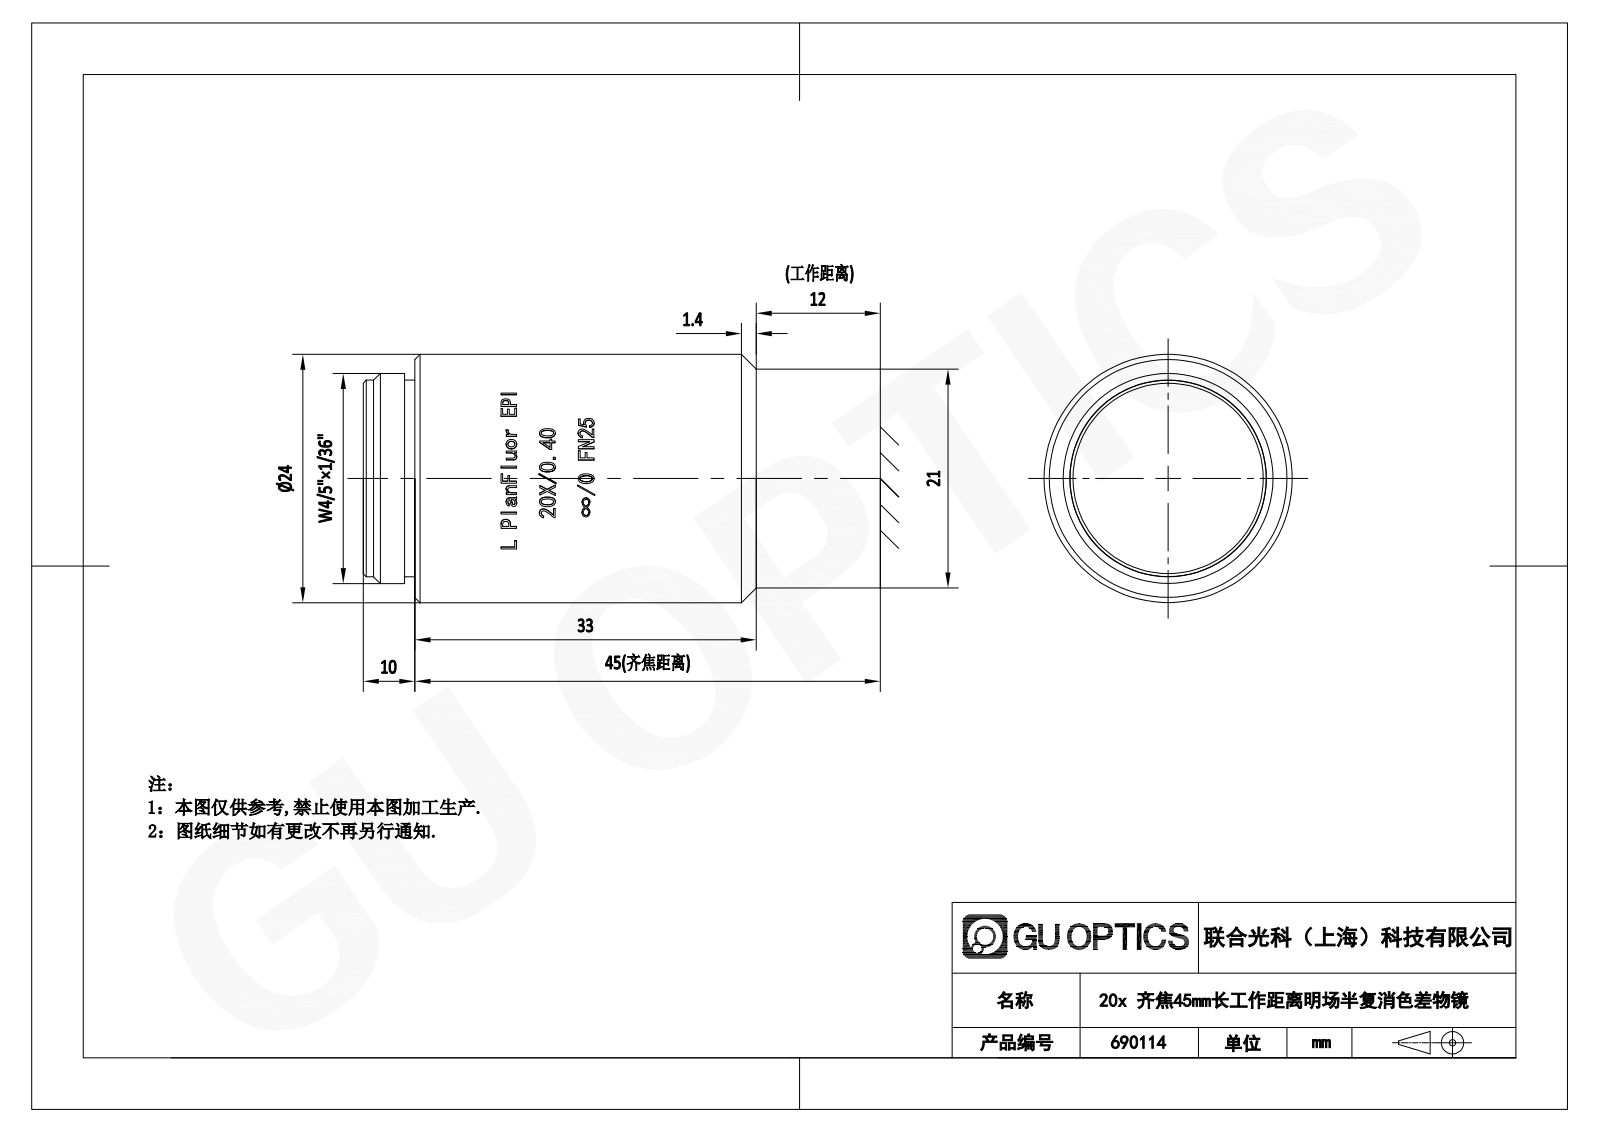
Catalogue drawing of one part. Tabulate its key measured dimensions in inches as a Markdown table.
| quantity | value |
| --- | --- |
| part name | 690114 |
| STEP written by | SolidWorks 2020 (CONFIG_CONTROL_DESIGN) |
| units | inches |
| bodies | 1 solid, 310 faces (142 planar, 47 cylindrical, 121 other) |
| overall size | 1.496 × 0.947 × 0.945 |
| volume | 0.999 in³ |
| surface area | 5.687 in² |
| round bosses / shafts (diameter × count) | 0.945 × 1, 0.8 × 1, 0.748 × 1 |
| partial cylindrical surfaces (radius × count) | 0.474 × 1 |
| main face-to-face distances | 1.496, 0.197, 1.299, 0.039, 0.157, 1.339, 0.118, 1.457, 0.583, 0.544 |
